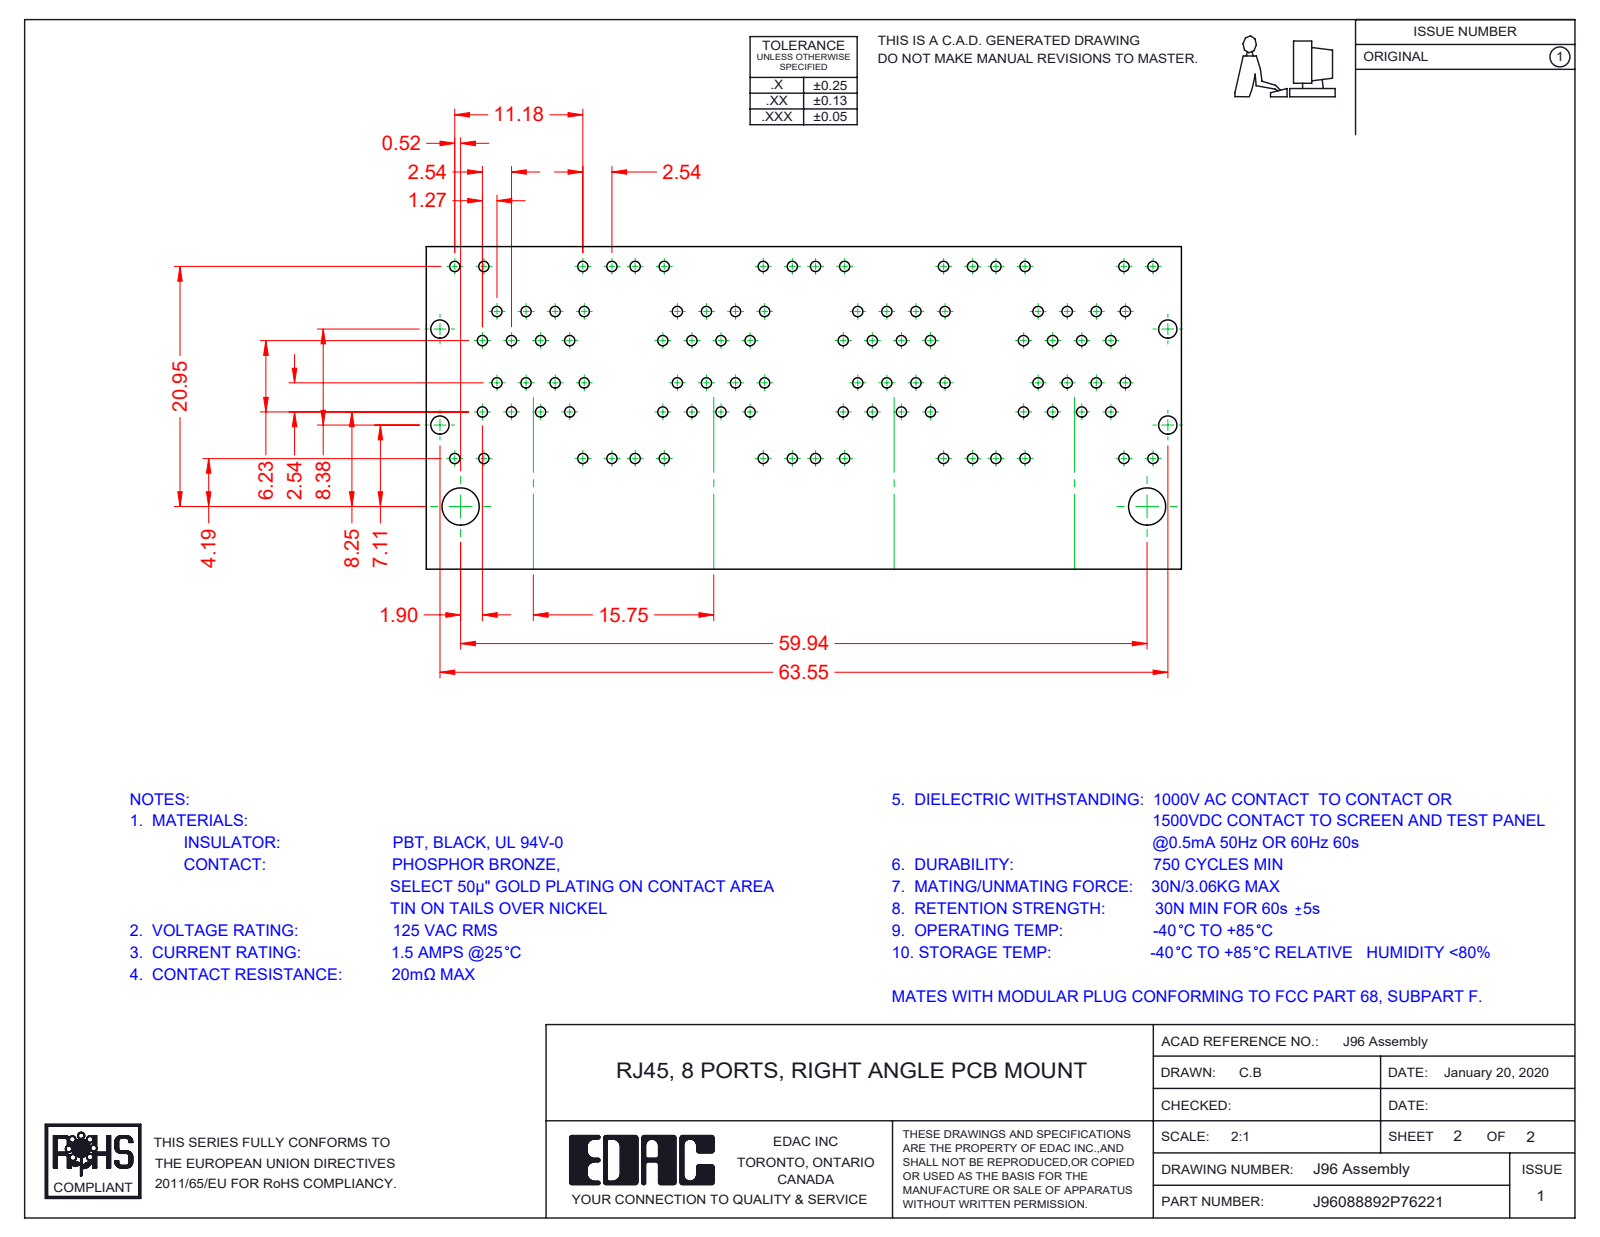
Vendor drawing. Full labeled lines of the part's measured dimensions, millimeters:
Part name (STEP PRODUCT): 96 LED RH Upper_6-Red-Green; 96 Back Plate_8 Ports; 96 Insulator_8 Ports; 96 LED LH Lower_7-Green-Orange (+8 more)
STEP written by: SolidWorks 2016 (CONFIG_CONTROL_DESIGN)
Units: millimetres
Bodies: 96 solids, 7836 faces (6105 planar, 1420 cylindrical, 311 other)
Overall size (bounding box): 67.35 × 31.38 × 28.68
Volume: 24 149 mm³ · Surface area: 63 596 mm²
Round holes (diameter × count): ⌀1.7 ×3
Round bosses / shafts (diameter × count): ⌀1.68 ×3
Partial cylindrical surfaces — rounded edges, fillets, slot ends (radius × count): R0.25 ×124, R0.35 ×73, R1 ×72, R0.5 ×49, R0.91 ×32, R0.2 ×27, R0.27 ×14, R0.7 ×11
Main face-to-face distances: 15.75, 0.35, 9.95, 1.17, 1.6, 0.54, 9.98, 10.18, 12.67, 3.37
Hole centre spacings: 15.75, 31.5
